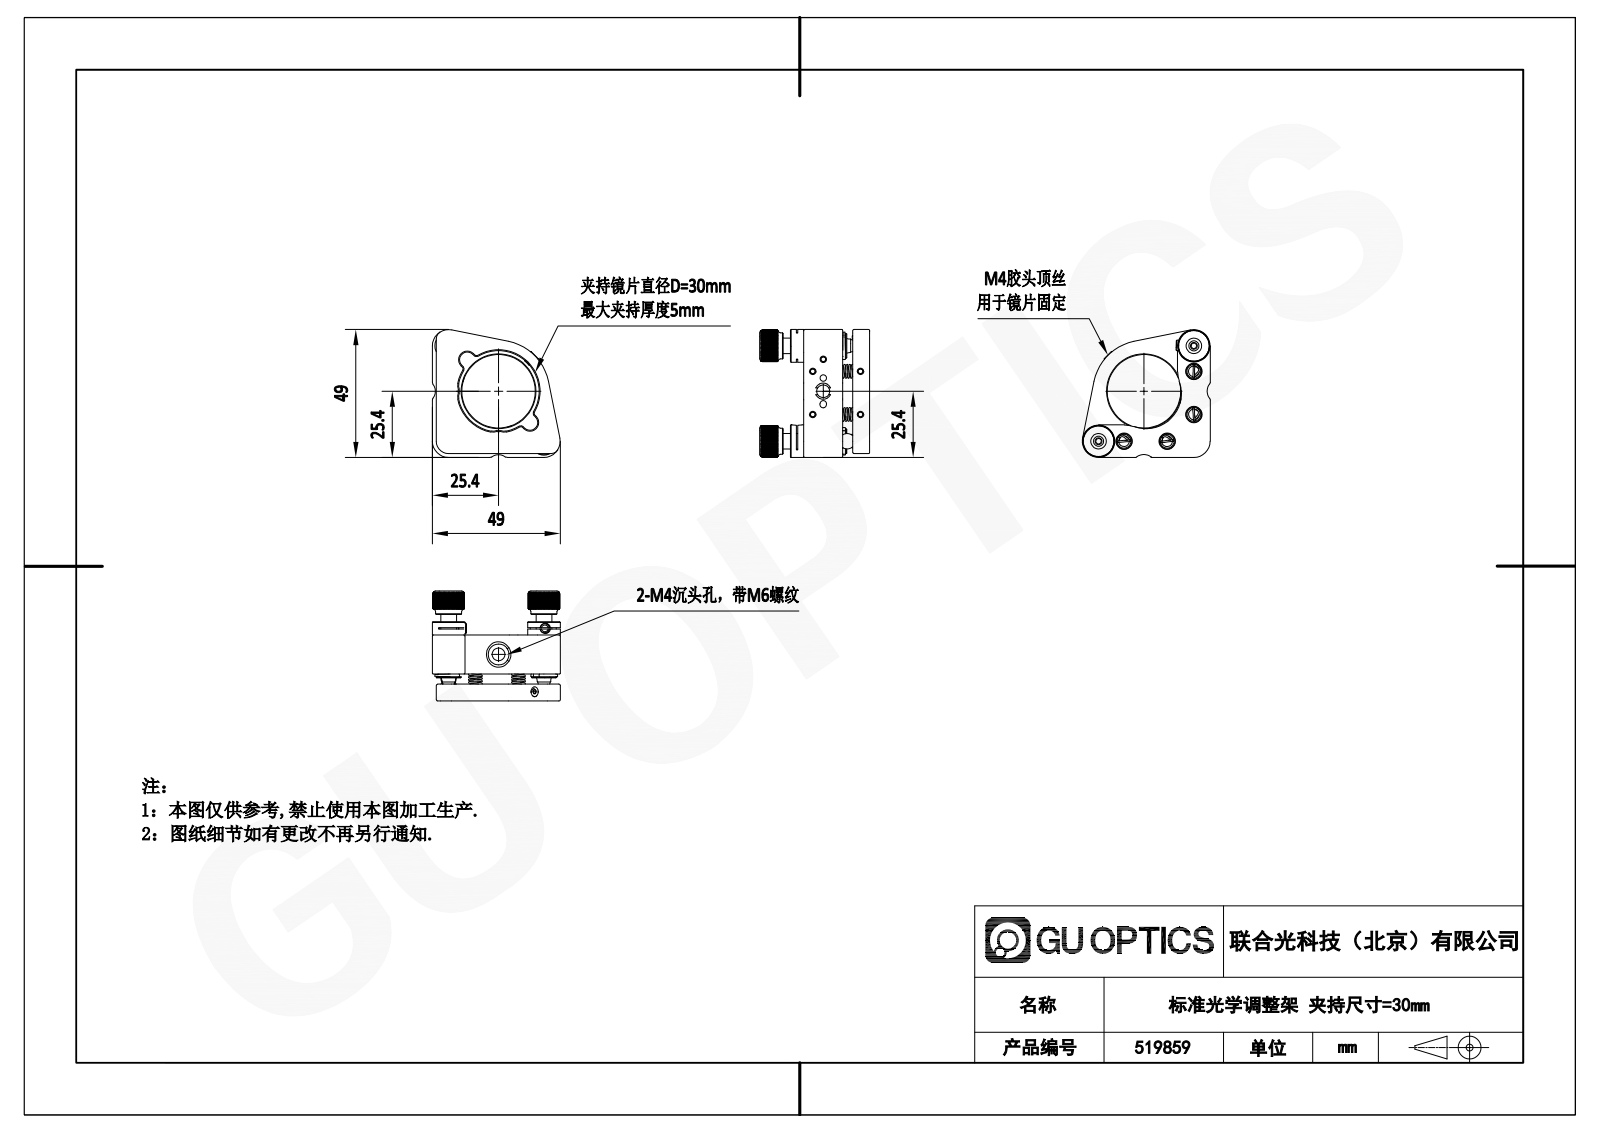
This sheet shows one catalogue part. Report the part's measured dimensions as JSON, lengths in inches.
{"part_name": "519859", "step_written_by": "SolidWorks 2020 (CONFIG_CONTROL_DESIGN)", "units": "inches", "bodies": {"solids": 0, "faces": 1194, "planar": 536, "cylindrical": 317, "other": 341}, "overall_size": [1.929, 1.929, 1.657], "round_holes": [[0.118, 10], [0.236, 6], [0.098, 4], [0.157, 3], [0.315, 3], [0.181, 2], [0.187, 2], [0.197, 2], [0.256, 2], [0.378, 2], [0.413, 2], [0.13, 1]], "round_bosses_or_shafts": [[0.059, 4], [0.492, 2], [0.394, 2], [0.374, 2], [0.094, 1]], "partial_cylinders_radius": [[0.02, 12], [0.049, 10], [0.006, 8], [0.012, 8], [0.039, 8], [0.079, 8], [0.157, 5], [0.031, 4]], "face_to_face_distances": [0.256, 0.15, 0.996, 0.74, 0.591, 0.406, 0.059, 0.039, 0.217, 0.433], "hole_center_spacings": [0.65, 0.72, 0.97, 0.188, 0.197, 0.24, 0.283, 0.338]}
